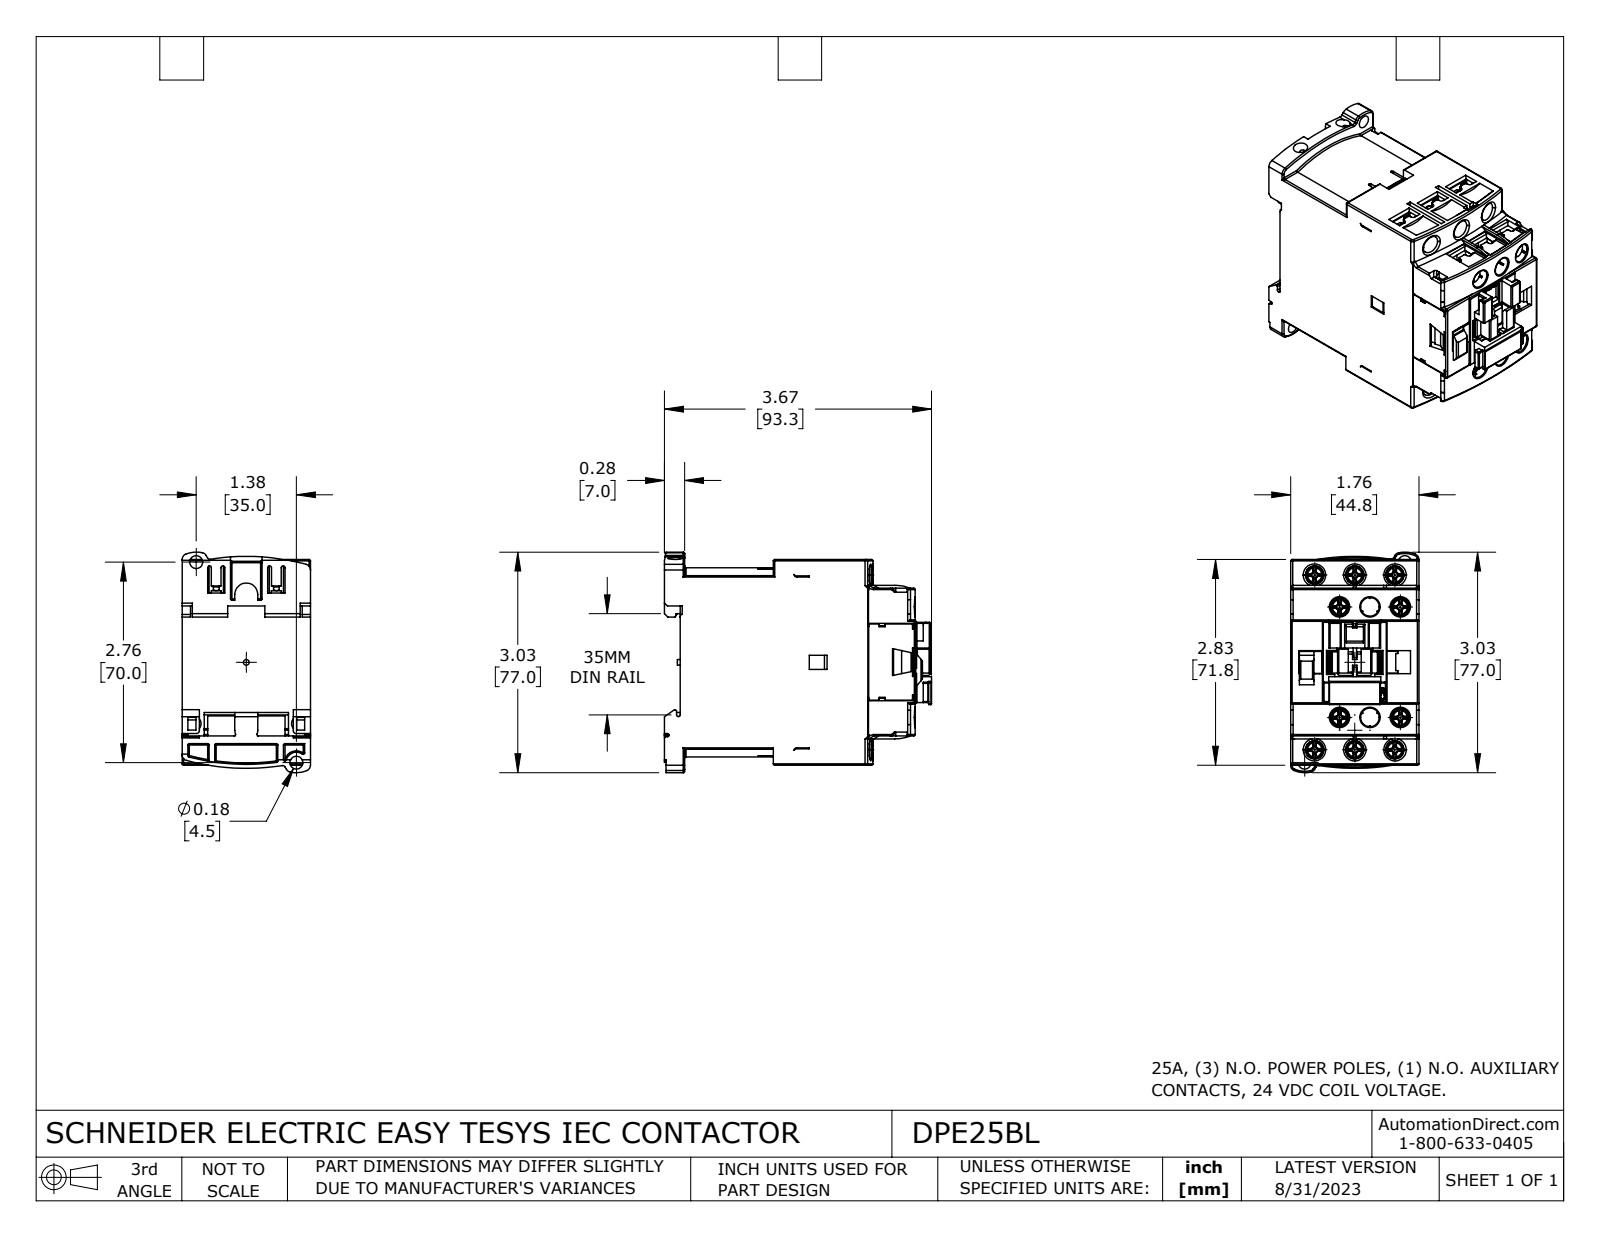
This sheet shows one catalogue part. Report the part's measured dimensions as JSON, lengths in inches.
{"part_name": "DPE25BL", "step_written_by": "SolidWorks 2021 (CONFIG_CONTROL_DESIGN)", "units": "inches", "bodies": {"solids": 10, "faces": 3575, "planar": 2470, "cylindrical": 705, "other": 400}, "overall_size": [3.671, 3.031, 1.764], "volume_in3": 12.53, "surface_area_in2": 94.96, "round_holes": [[0.252, 6], [0.256, 6], [0.039, 2], [0.177, 2], [0.197, 2], [0.098, 1], [0.167, 1], [0.236, 1]], "round_bosses_or_shafts": [[0.138, 10], [0.108, 10], [0.315, 6], [0.157, 2], [0.079, 1]], "partial_cylinders_radius": [[0.02, 91], [0.006, 42], [0.039, 34], [0.012, 31], [0.016, 22], [0.008, 14], [0.031, 10], [0.157, 9]], "face_to_face_distances": [1.764, 0.272, 2.579, 2.555, 0.047, 0.217, 0.15, 2.283, 1.717, 0.173], "hole_center_spacings": [0.417, 0.551, 1.576, 2.464, 1.52, 2.402, 0.224, 0.274]}
